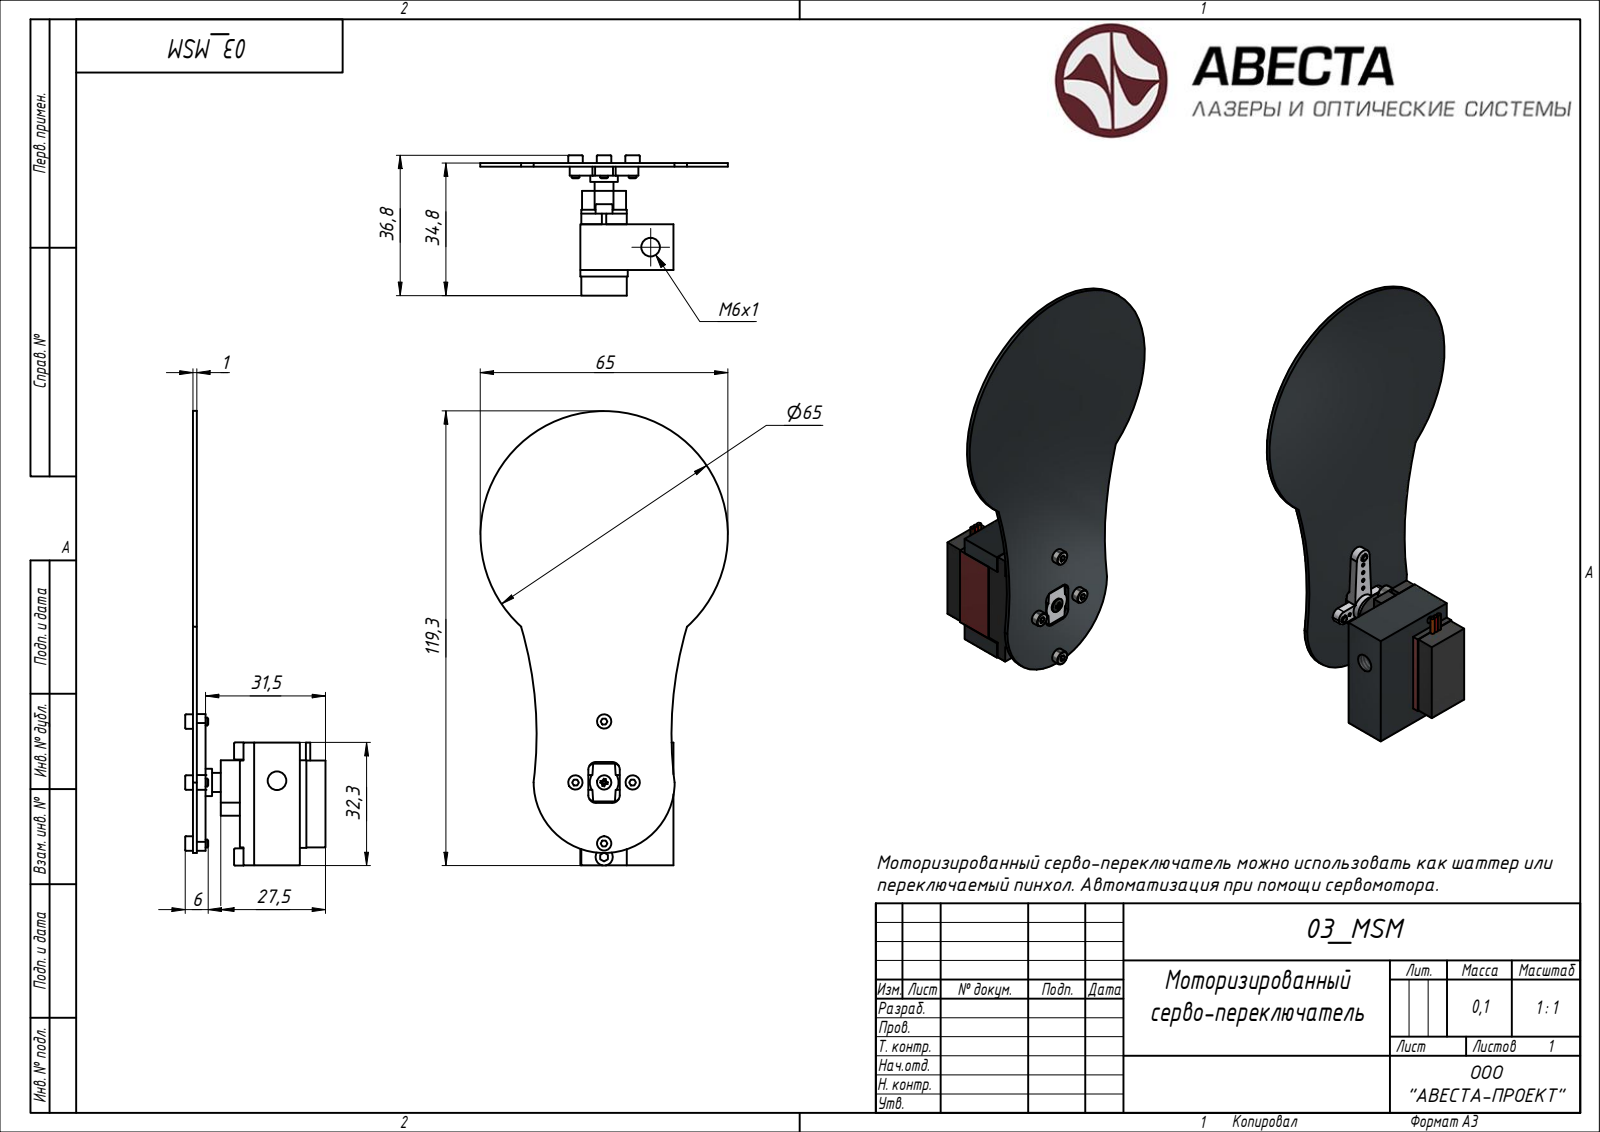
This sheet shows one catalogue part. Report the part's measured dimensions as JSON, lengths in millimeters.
{"step_written_by": "Rhino 7.34 (AUTOMOTIVE_DESIGN)", "units": "millimeters", "bodies": {"solids": 1, "faces": 288, "planar": 151, "cylindrical": 80, "other": 57}, "overall_size": [119.3, 65, 36.8], "volume_mm3": 18555, "surface_area_mm2": 16003, "round_holes": [[1, 10], [2.01, 2], [4.92, 1], [4.92, 1]], "round_bosses_or_shafts": [[3.8, 5], [2, 4], [1.17, 3], [4.5, 2], [11.6, 1], [7.2, 1], [5, 1]], "partial_cylinders_radius": [[1.9, 4], [2, 4], [1.25, 2], [2.35, 2], [100, 2], [2.5, 1], [3.75, 1], [18.5, 1]], "face_to_face_distances": [1, 12, 12.25, 27.1, 28.1, 15.1, 16.1, 24.5, 27.5, 32.2], "hole_center_spacings": [2.5, 5, 7.81, 9.86, 12.08, 14.4, 19.5, 17]}
